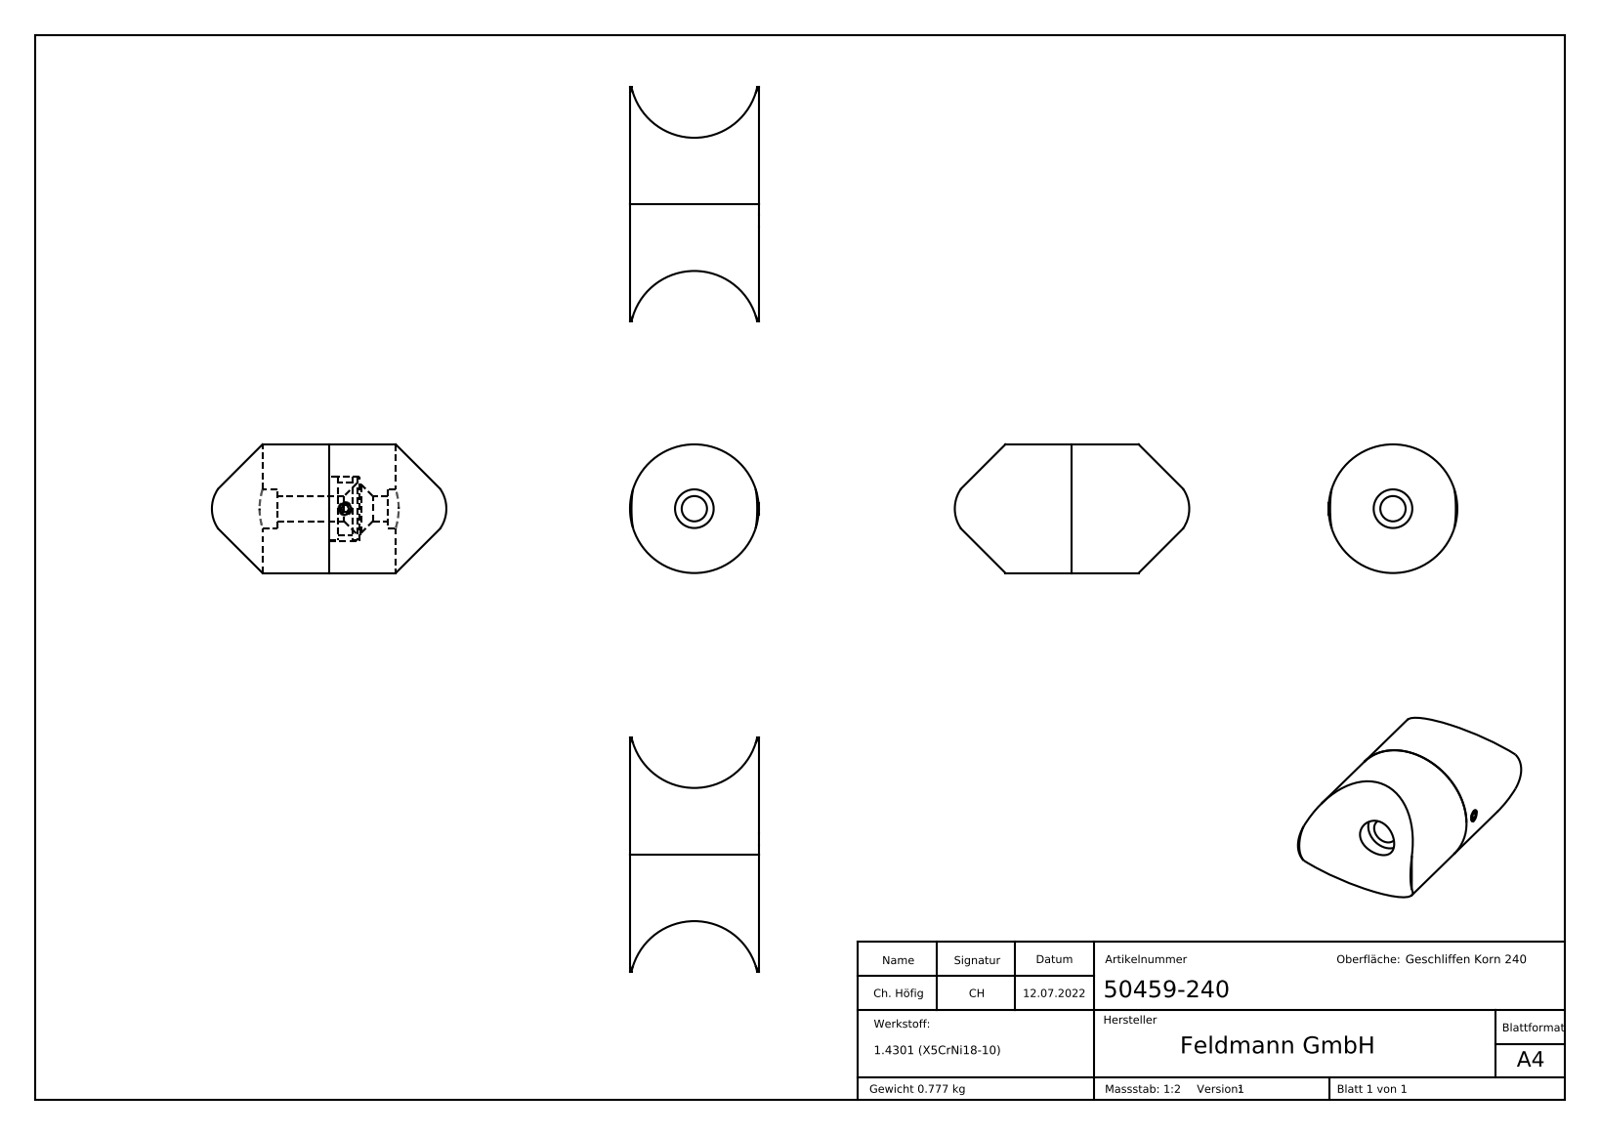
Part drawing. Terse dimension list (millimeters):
name: 50459-240 Teil2_50459-240 Teil2; 50459-240; 50459-240 DIN913 M5x10_DIN913 M5x10; 50459-240 Teil1_50459-240 Teil1
written by: SolidWorks 2018 (CONFIG_CONTROL_DESIGN)
unit: mm
bodies: 3 solids, 267 faces (147 planar, 19 cylindrical, 101 other)
size: 88 × 48.3 × 48.3
volume: 98 363 mm³; area: 21 809 mm²
holes: 1× ⌀4.2, 1× ⌀9.5, 1× ⌀14.5, 1× ⌀18.25, 1× ⌀24
bosses: 1× ⌀48.3, 1× ⌀23.75, 1× ⌀19.75, 1× ⌀5
rounds: 2× R13.14, 2× R24.15
face distances: 11.5, 10.5, 1, 2.7, 1.7, 8.8, 8.2, 7.2, 5.5, 3.3
